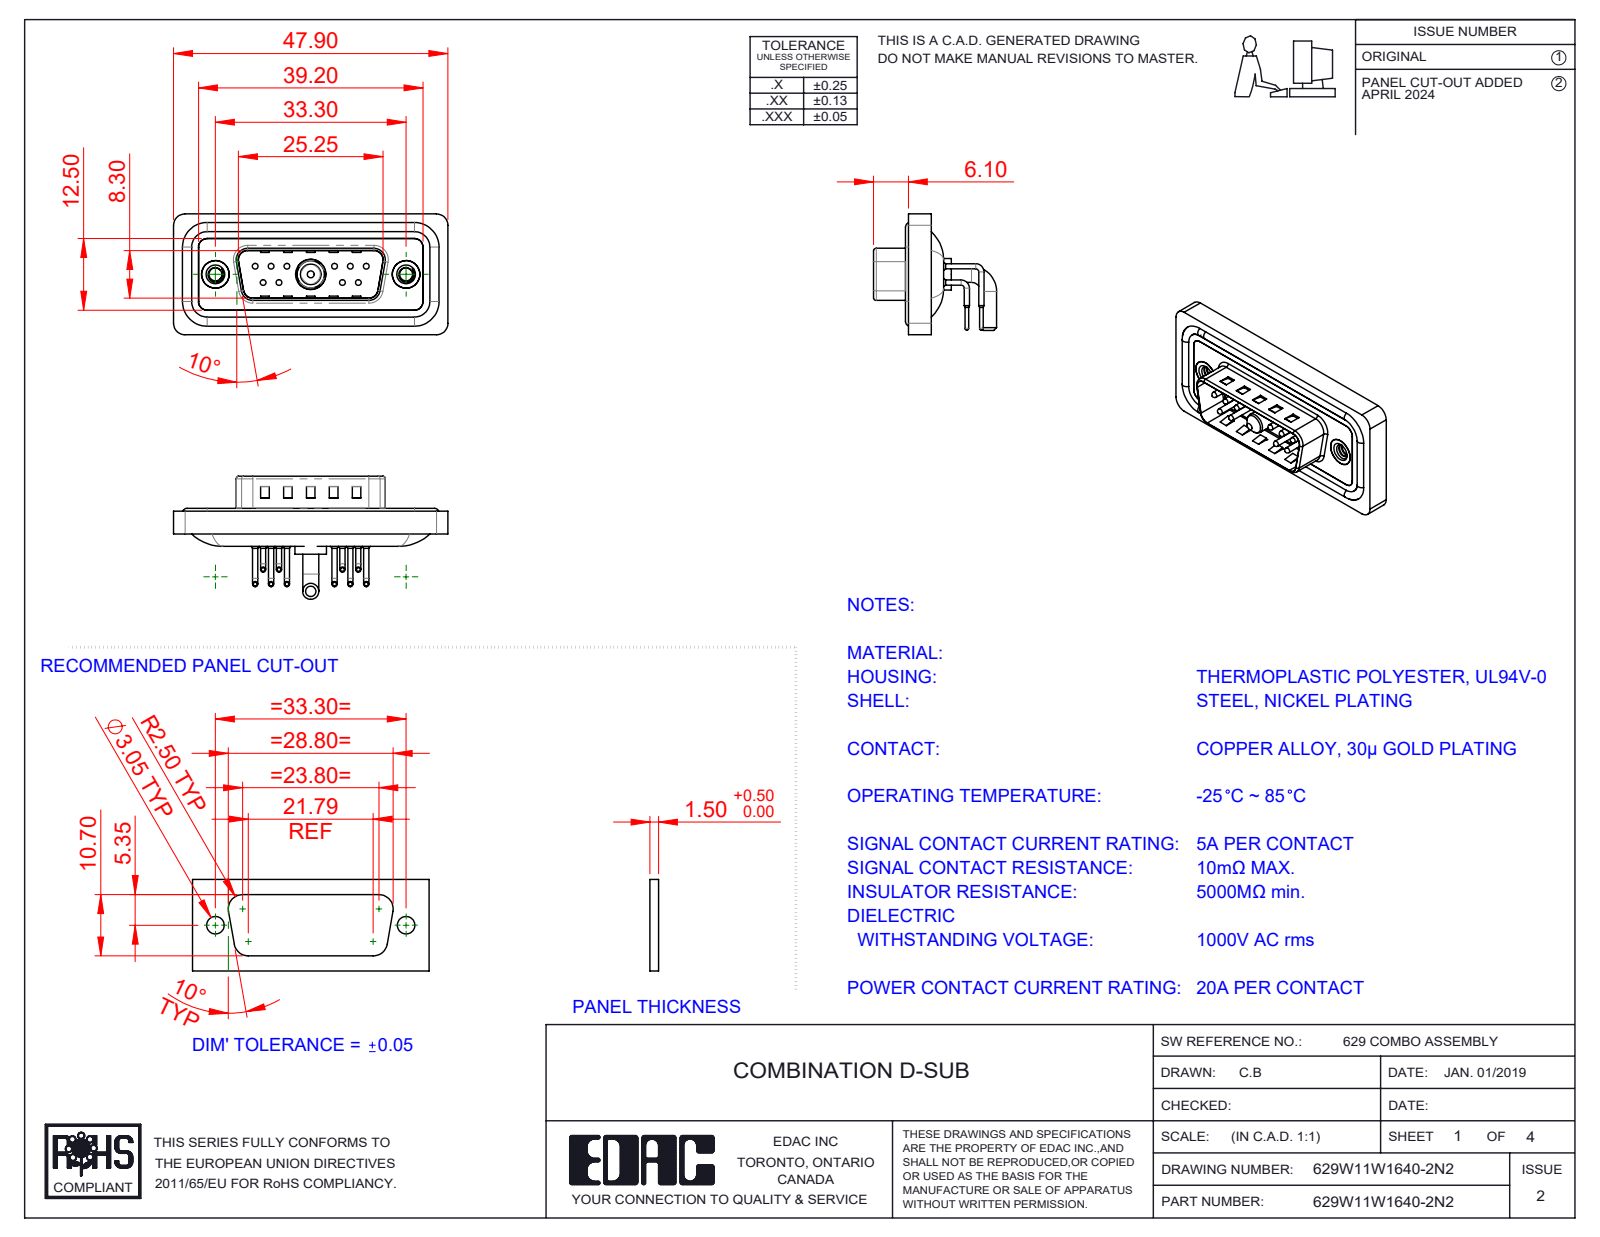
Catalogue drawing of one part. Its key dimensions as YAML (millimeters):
part_name: "629Combo Waterproof Housing_15 Contacts; 629Combo Contact Row 1; 629W11W1640-2N2; Power Pin_20A RA (+5 more)"
step_written_by: "SolidWorks 2023 (CONFIG_CONTROL_DESIGN)"
units: millimeters
bodies: {solids: 19, faces: 1603, planar: 836, cylindrical: 569, other: 198}
overall_size: [47.9, 21.5, 21.1]
volume: 5600
surface_area: 9280
round_holes:
  - {diameter: 0.75, count: 10}
  - {diameter: 1.6, count: 10}
  - {diameter: 2, count: 10}
  - {diameter: 2.26, count: 2}
  - {diameter: 4, count: 2}
  - {diameter: 4.8, count: 2}
  - {diameter: 5, count: 2}
  - {diameter: 4.85, count: 1}
  - {diameter: 5.3, count: 1}
round_bosses_or_shafts:
  - {diameter: 0.9, count: 20}
  - {diameter: 1.5, count: 10}
  - {diameter: 1, count: 10}
  - {diameter: 0.65, count: 10}
  - {diameter: 1.6, count: 4}
  - {diameter: 4.9, count: 2}
  - {diameter: 2.8, count: 2}
  - {diameter: 5.5, count: 1}
partial_cylinders:
  - {radius: 2, count: 20}
  - {radius: 1.5, count: 18}
  - {radius: 1.01, count: 10}
  - {radius: 0.5, count: 8}
  - {radius: 1.6, count: 8}
  - {radius: 1, count: 7}
  - {radius: 0.25, count: 4}
  - {radius: 0.6, count: 4}
face_to_face_distances: [0.4, 2.9, 0.8, 1.1, 2.1, 1.6, 2.5, 4.1, 4.5, 3.1]
hole_center_spacings: [3.16, 2.77, 13.85, 11.08, 16.62, 5.03, 5.04, 5.54]
